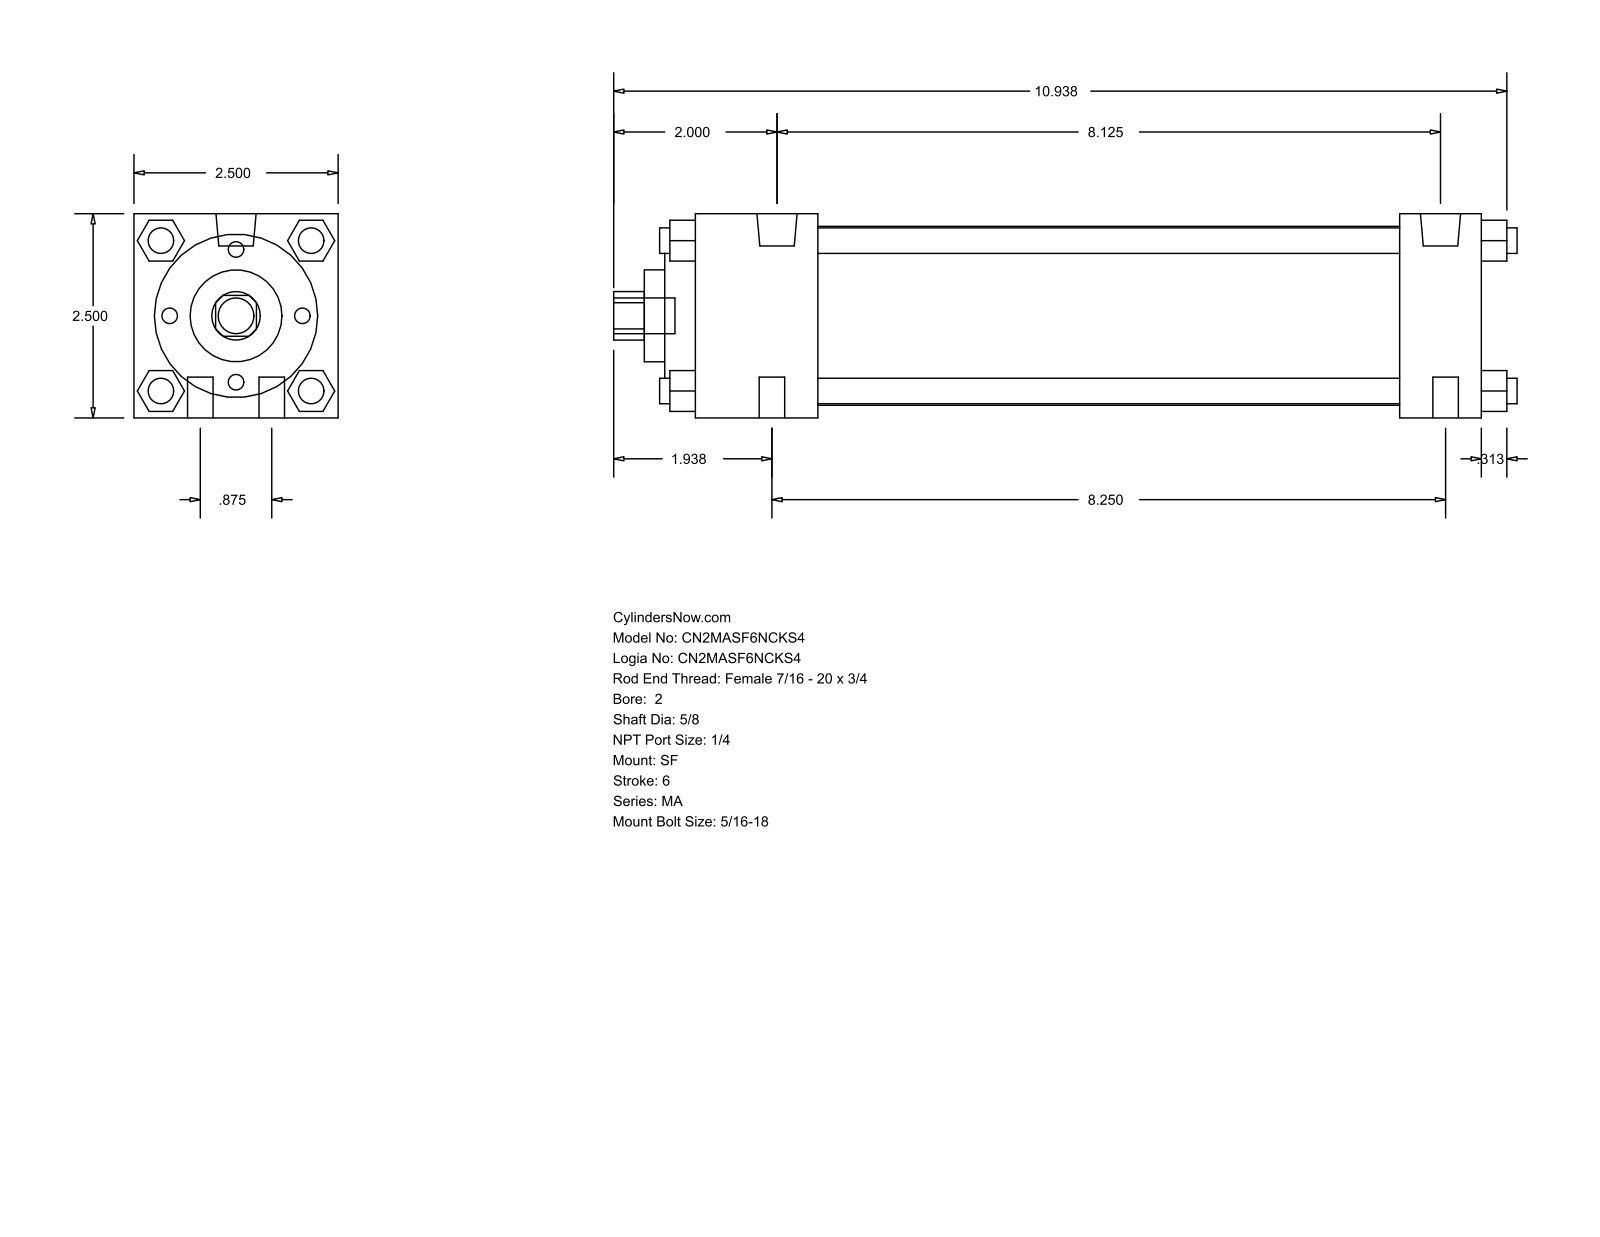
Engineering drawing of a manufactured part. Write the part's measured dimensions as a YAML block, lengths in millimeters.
part_name: "MA_SF__0200_0.625"
step_written_by: "GSSL Pune (CONFIG_CONTROL_DESIGN)"
units: millimeters
bodies: {solids: 0, faces: 126, planar: 95, cylindrical: 31, other: 0}
overall_size: [280.99, 63.5, 63.5]
round_holes:
  - {diameter: 15.88, count: 1}
  - {diameter: 28.57, count: 1}
  - {diameter: 50.8, count: 1}
  - {diameter: 55.63, count: 1}
round_bosses_or_shafts:
  - {diameter: 7.94, count: 10}
  - {diameter: 12.49, count: 2}
  - {diameter: 11.11, count: 1}
partial_cylinders:
  - {radius: 7.54, count: 1}
face_to_face_distances: [63.5, 12.7, 38.1, 9.52, 244.48, 219.07, 25.41, 180.97, 206.38, 47.62]
